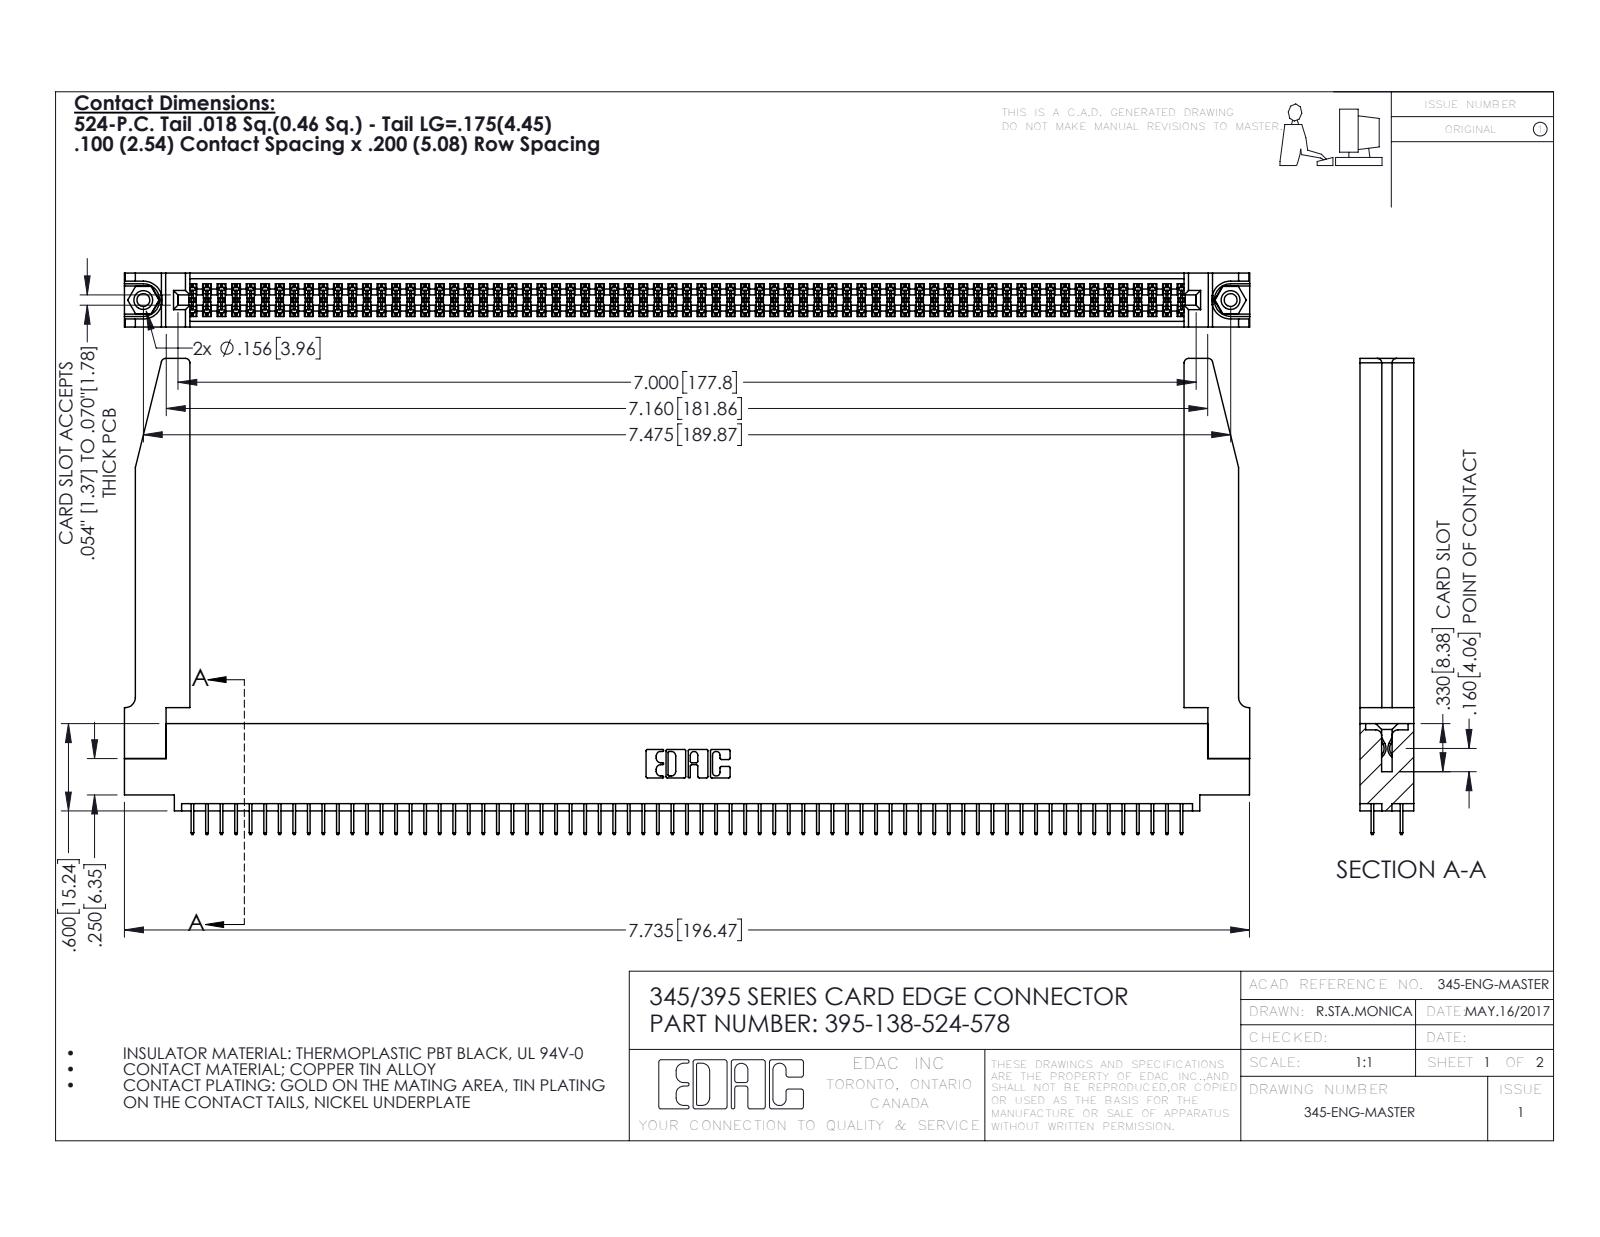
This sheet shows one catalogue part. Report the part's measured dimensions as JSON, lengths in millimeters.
{"part_name": "345 Part_0.110 Offset - 0.156 Dia-TH; 345-250-001_345-250-001-102; 395-138-524-578; 345-220-078_345-220-078 (+1 more)", "step_written_by": "SolidWorks 2016 (CONFIG_CONTROL_DESIGN)", "units": "millimeters", "bodies": {"solids": 143, "faces": 7816, "planar": 5608, "cylindrical": 2156, "other": 52}, "overall_size": [196.5, 83.1, 9.4], "volume_mm3": 26830, "surface_area_mm2": 35070, "round_holes": [[2.3, 2], [3.2, 2], [4, 2], [1.6, 1]], "round_bosses_or_shafts": [[3.9, 2]], "partial_cylinders_radius": [[0.2, 207], [0.3, 22], [0.8, 8], [0.2, 6], [0.8, 6], [0.7, 3], [0.4, 2], [0.5, 2]], "face_to_face_distances": [1.8, 7.6, 9.4, 5.1, 2.5, 6.9, 0.6, 5.7, 1.8, 4.4], "hole_center_spacings": [6.9, 183.9, 189.9]}
